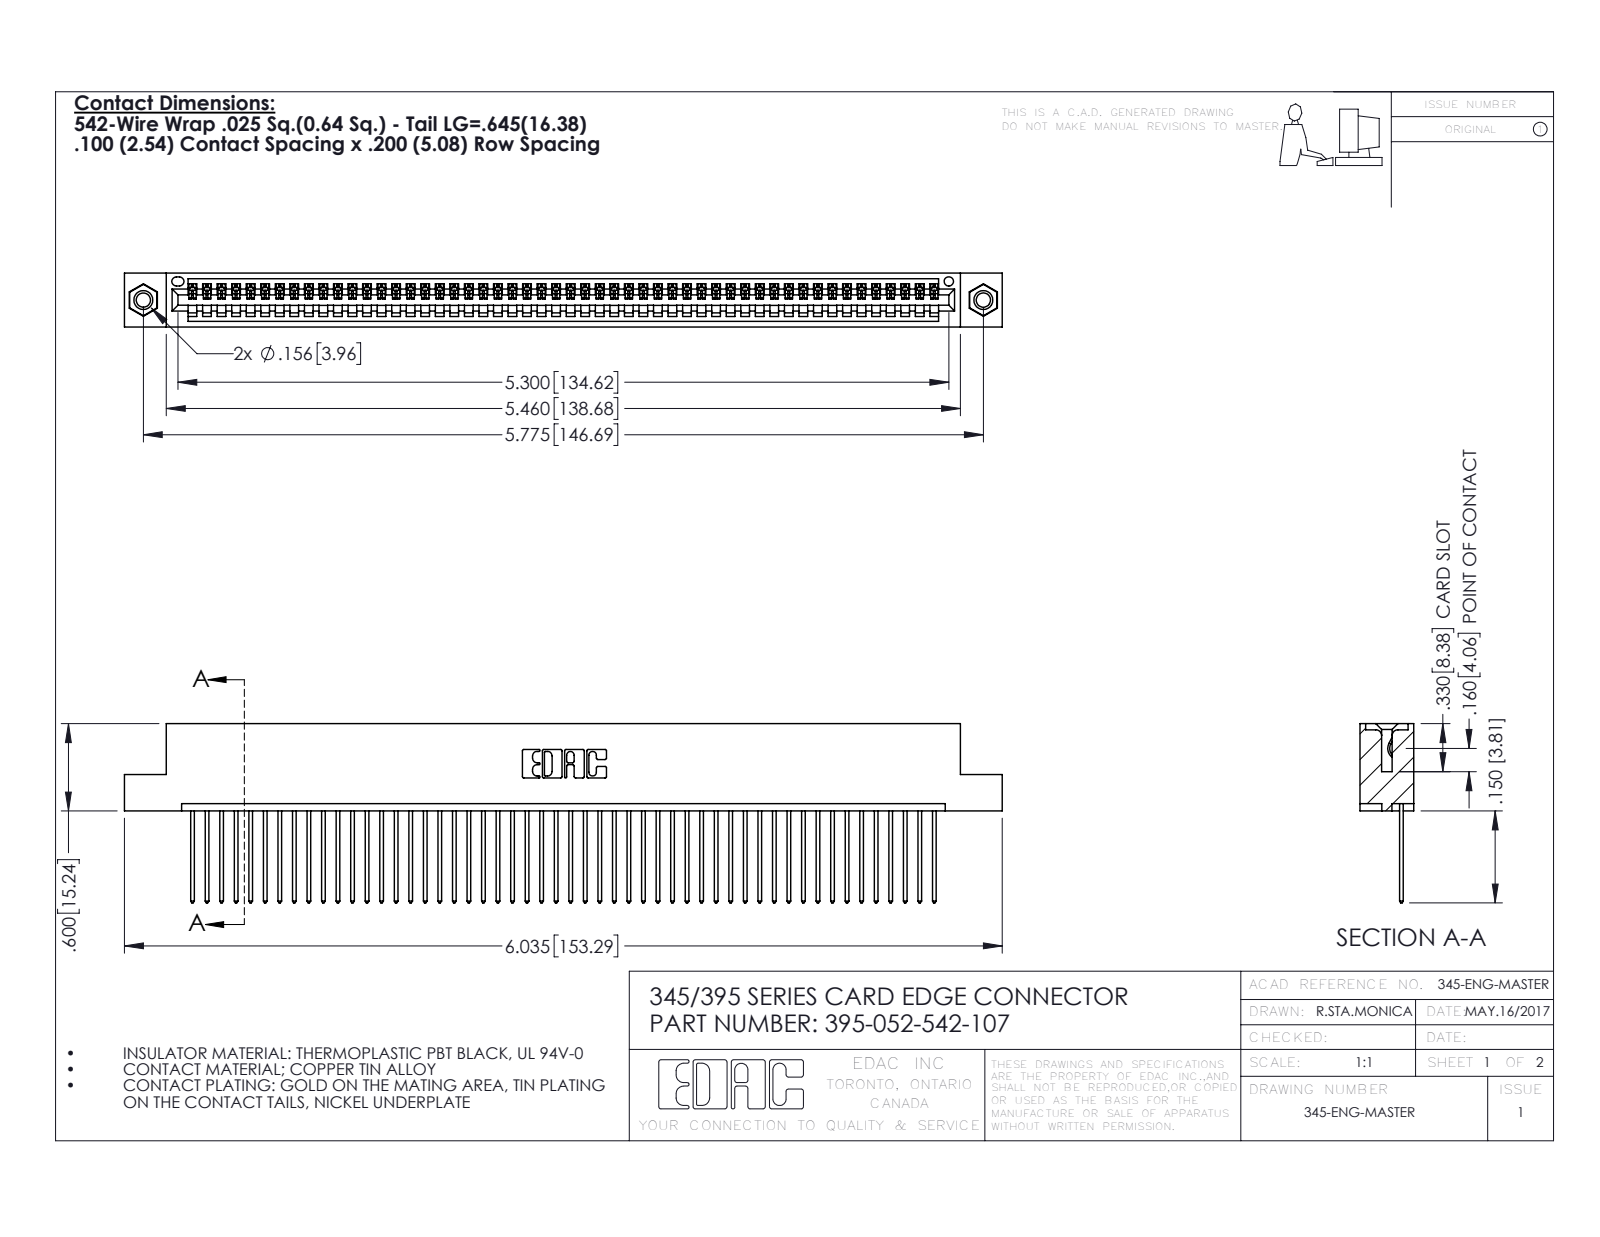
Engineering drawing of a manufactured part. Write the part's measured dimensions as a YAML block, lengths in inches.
part_name: "345-292-001_345-293-142; 395-052-542-107; 345 Part_Flush Mounting Lugs - 0.156 Dia-TI; 345-250-001_345-250-005-103"
step_written_by: "SolidWorks 2016 (CONFIG_CONTROL_DESIGN)"
units: inches
bodies: {solids: 55, faces: 3202, planar: 2192, cylindrical: 994, other: 16}
overall_size: [6.035, 1.232, 0.37]
volume: 0.9
surface_area: 31.76
round_holes:
  - {diameter: 0.098, count: 2}
  - {diameter: 0.125, count: 2}
  - {diameter: 0.156, count: 2}
  - {diameter: 0.064, count: 1}
round_bosses_or_shafts:
  - {diameter: 0.155, count: 2}
partial_cylinders:
  - {radius: 0.006, count: 104}
  - {radius: 0.01, count: 104}
  - {radius: 0.01, count: 22}
  - {radius: 0.007, count: 6}
  - {radius: 0.031, count: 6}
  - {radius: 0.026, count: 3}
  - {radius: 0.031, count: 2}
  - {radius: 0.04, count: 2}
face_to_face_distances: [0.072, 0.298, 0.098, 0.272, 0.025, 0.37, 0.2, 0.225, 0.149, 0.072]
hole_center_spacings: [0.27, 5.539, 5.775]
